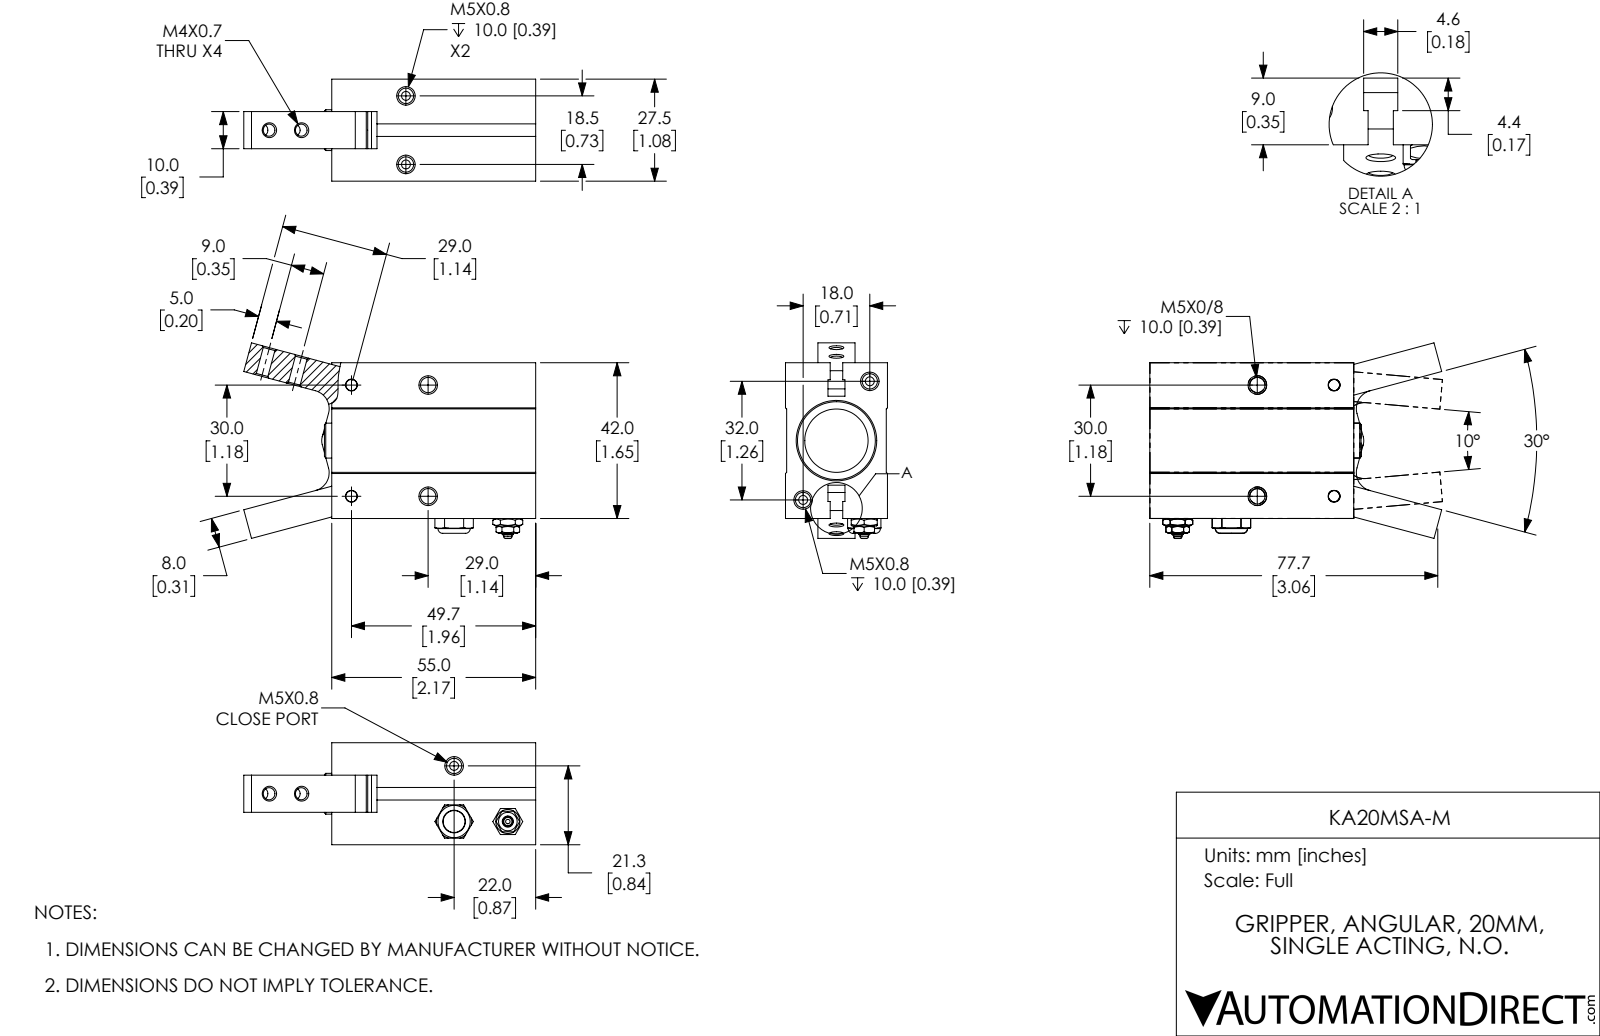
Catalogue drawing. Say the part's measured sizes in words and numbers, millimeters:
The part is named "KA20MSA-M-1; KA20MSA-M-2; KA20MSA-M-3; KA20MSA-M-4 (+1 more)". Its 3-D file was written by "SolidWorks 2017 (AUTOMOTIVE_DESIGN)". It is 4 solids with 294 faces: 114 planar, 92 cylindrical and 88 other. Overall it measures 78.75 by 52.77 by 27.5 millimeters. Its volume is 54 077 cubic millimeters and its surface area 23 143 square millimeters. Round holes: 8 of diameter 4.13, 4 of diameter 3.24, 2 of diameter 3, 2 of diameter 5.2, 1 of diameter 2.5, 1 of diameter 12, 1 of diameter 17.1, 1 of diameter 20, 1 of diameter 21, 1 of diameter 22. Round bosses or shafts: 1 of diameter 19.9, 1 of diameter 11, 1 of diameter 8.7, 1 of diameter 8, 1 of diameter 3, 1 of diameter 2.2. Partial cylindrical surfaces (rounded edges, fillets, slot ends): 2 of radius 4, 2 of radius 5. The main face-to-face distances are 27.2, 8.75, 18.75, 8.45, 18.45, 27.5, 42, 26.9, 6.7, 10. The hole center spacings are 9, 13.12, 15.52, 18.36, 20.7, 21.2, 28.9, 30.
